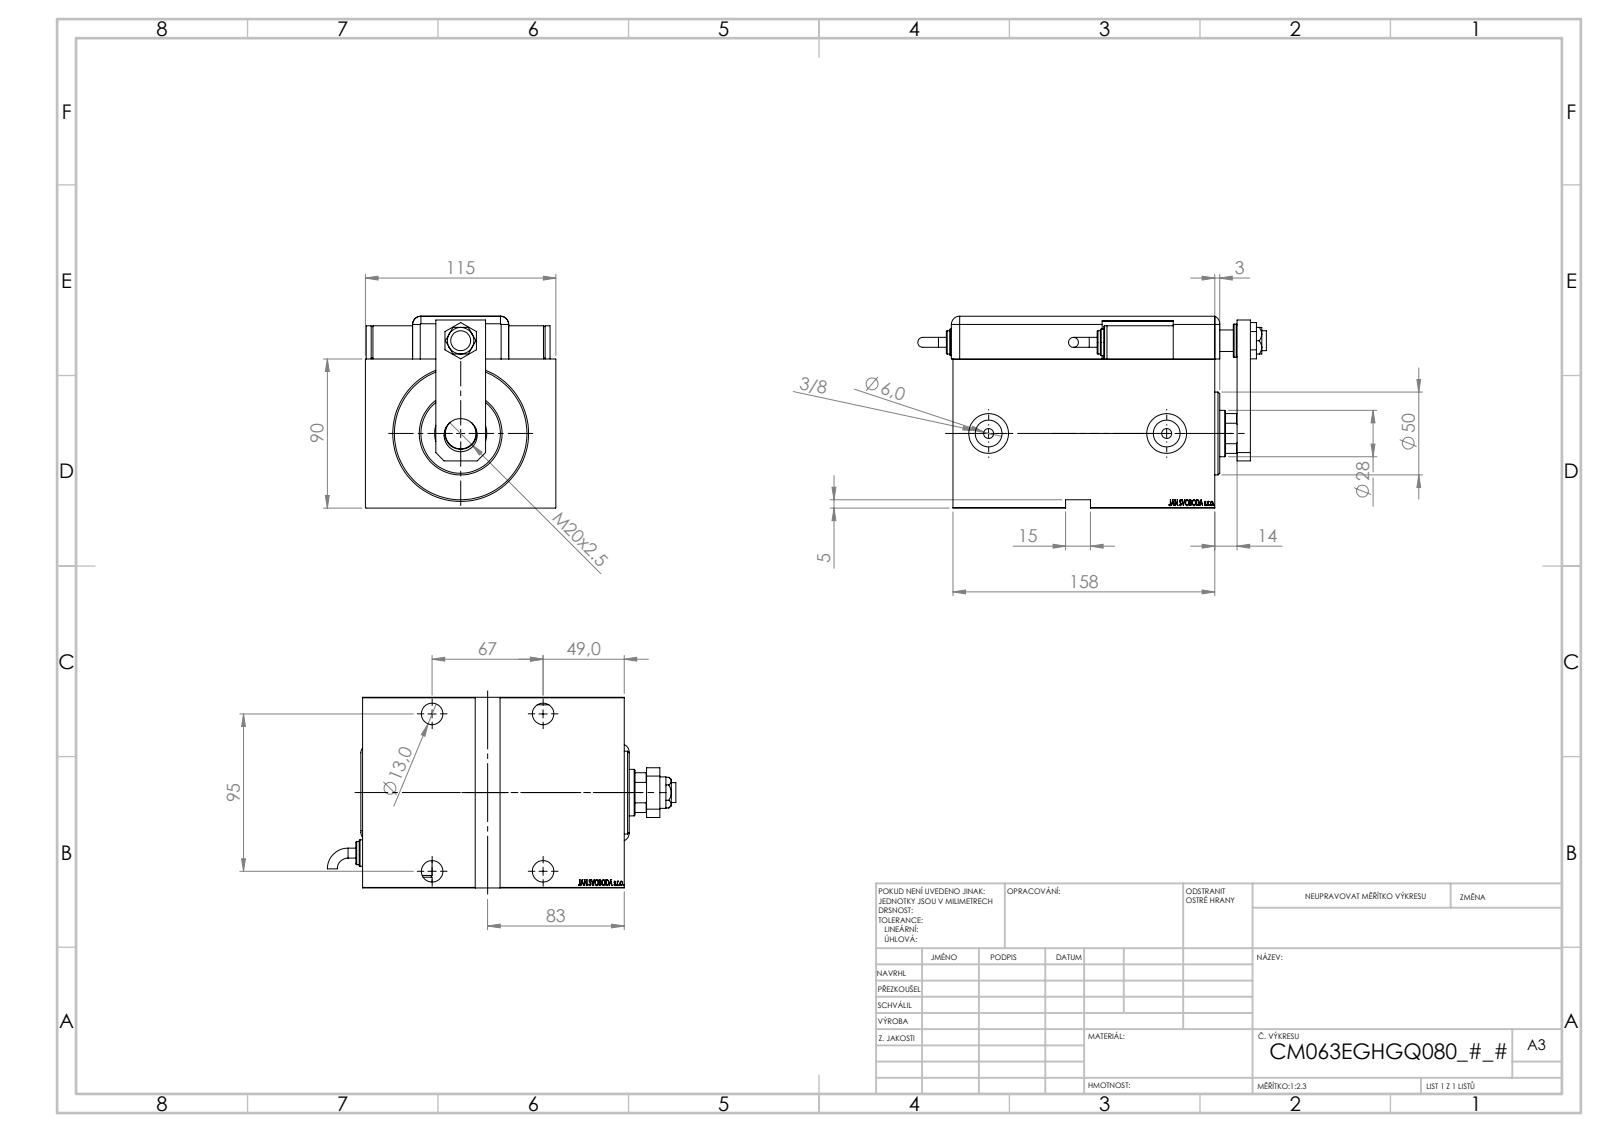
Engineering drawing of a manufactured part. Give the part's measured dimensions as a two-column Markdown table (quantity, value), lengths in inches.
| quantity | value |
| --- | --- |
| part name | KRYT; ZARAZKA_Q; V450CM_VC_B; V450CM_E_Body (+7 more) |
| STEP written by | SolidWorks 2019 (CONFIG_CONTROL_DESIGN) |
| units | inches |
| bodies | 13 solids, 1243 faces (617 planar, 109 cylindrical, 517 other) |
| overall size | 8.286 × 4.559 × 4.528 |
| volume | 91.47 in³ |
| surface area | 373.2 in² |
| round holes (diameter × count) | 0.512 × 5, 0.748 × 4, 0.157 × 2, 0.236 × 2, 0.315 × 2, 0.637 × 2, 0.945 × 2, 0.472 × 1, 0.551 × 1, 0.728 × 1, 0.787 × 1, 1.102 × 1 |
| round bosses / shafts (diameter × count) | 0.787 × 3, 0.63 × 2, 0.551 × 2, 0.236 × 2, 1.969 × 1 |
| partial cylindrical surfaces (radius × count) | 0.197 × 9, 0.394 × 1, 0.531 × 1 |
| main face-to-face distances | 3.543, 0.118, 4.528, 6.22, 4.559, 1.016, 0.689, 5.531, 1.122, 0.898 |
| hole center spacings | 2.202, 2.638, 2.792, 3.74, 4.52, 4.577, 4.834, 0.039 |
